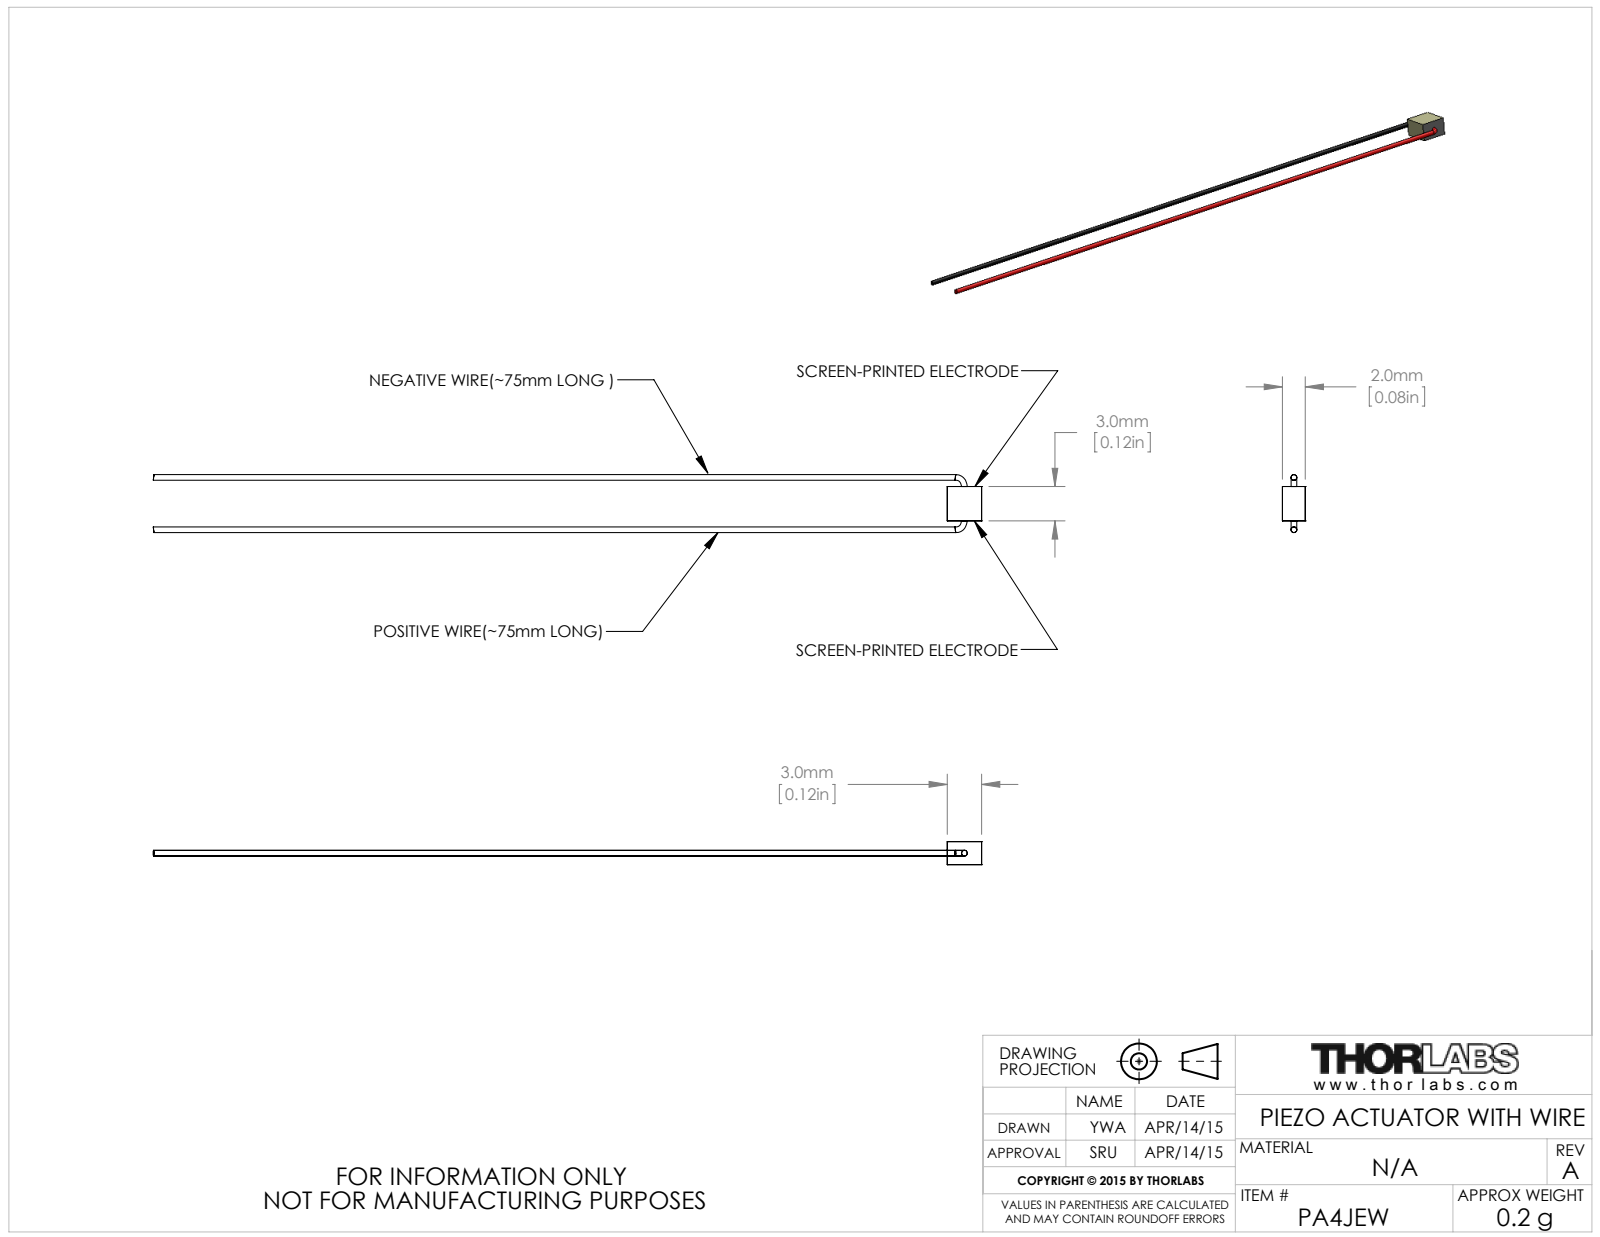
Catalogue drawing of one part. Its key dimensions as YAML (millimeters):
part_name: "CTN002956"
step_written_by: "SolidWorks 2014 (AUTOMOTIVE_DESIGN)"
units: millimeters
bodies: {solids: 1, faces: 16, planar: 8, cylindrical: 0, other: 8}
overall_size: [72.33, 5.06, 2]
volume: 46
surface_area: 265
face_to_face_distances: [3, 2]
